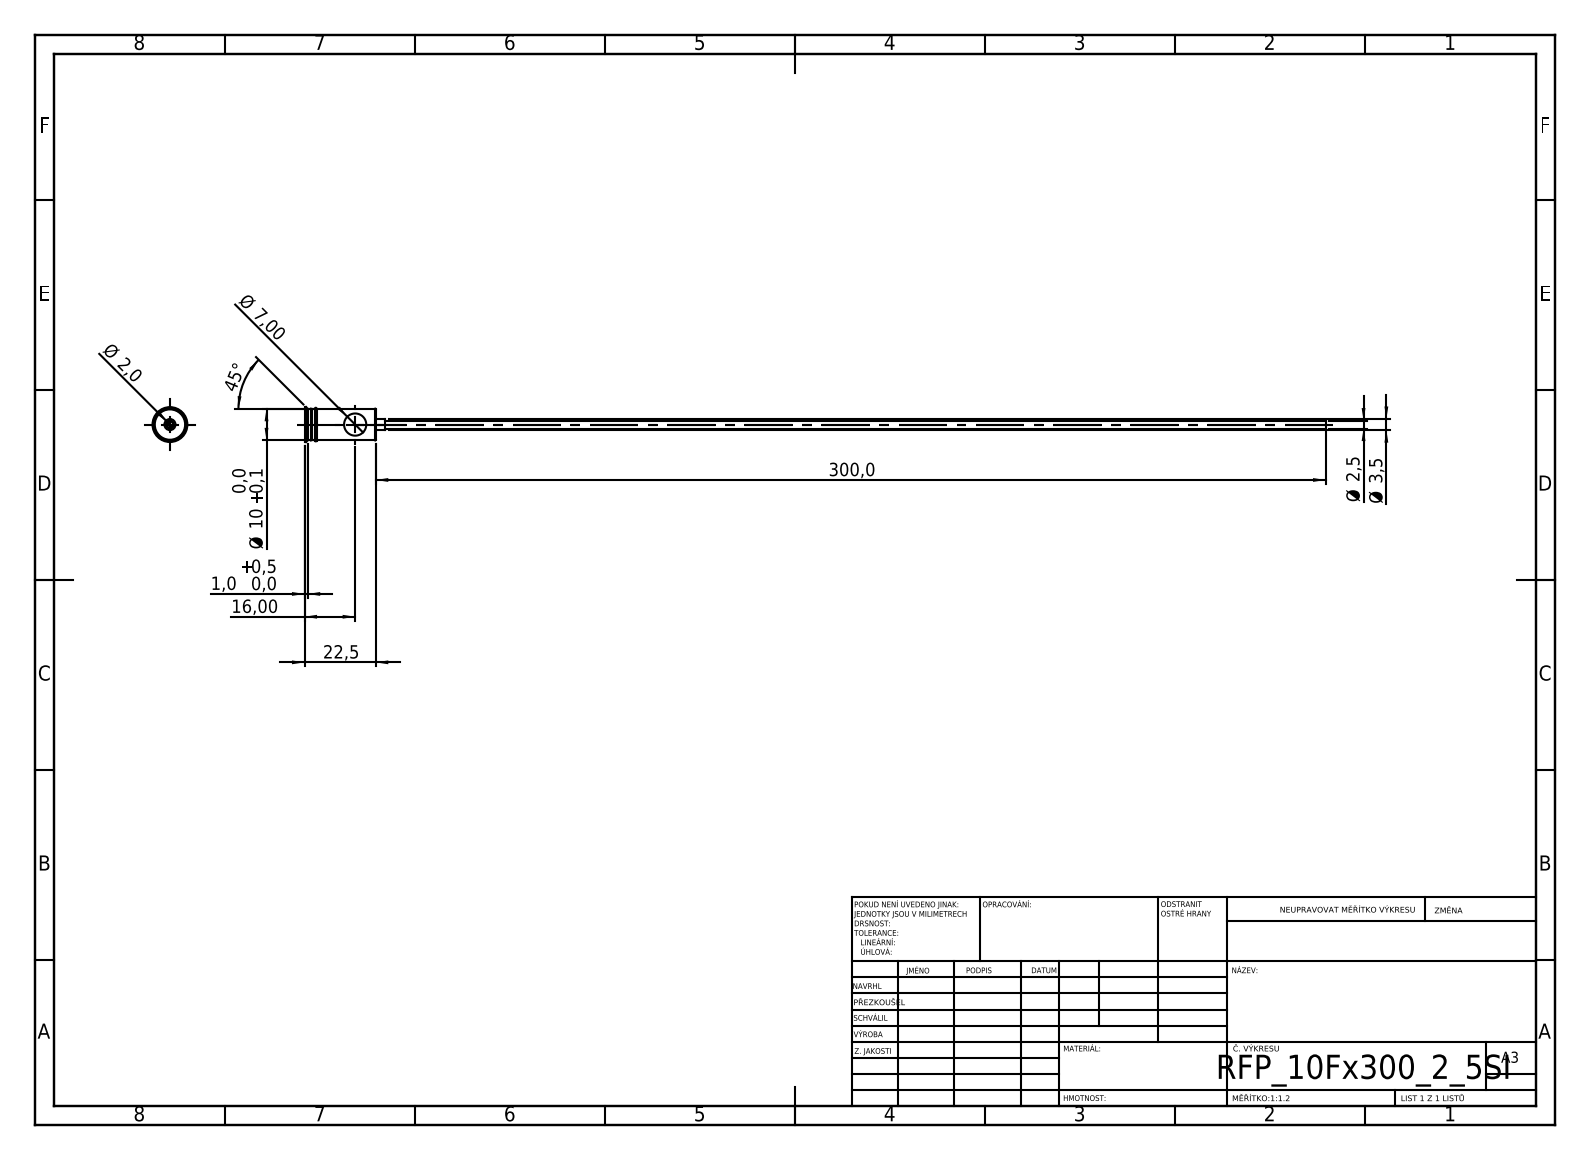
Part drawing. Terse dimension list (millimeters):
written by: SolidWorks 2019 (CONFIG_CONTROL_DESIGN)
unit: mm
bodies: 1 solid, 44 faces (20 planar, 16 cylindrical, 8 other)
size: 322.5 × 11 × 11
volume: 1 906 mm³; area: 5 317 mm²
holes: 1× ⌀2, 1× ⌀7
bosses: 1× ⌀11, 1× ⌀10, 1× ⌀3.5, 1× ⌀2.5
face distances: 22.5, 20.5, 2, 5.4, 20.2, 2.3, 3, 23.2, 23.5, 25.5
